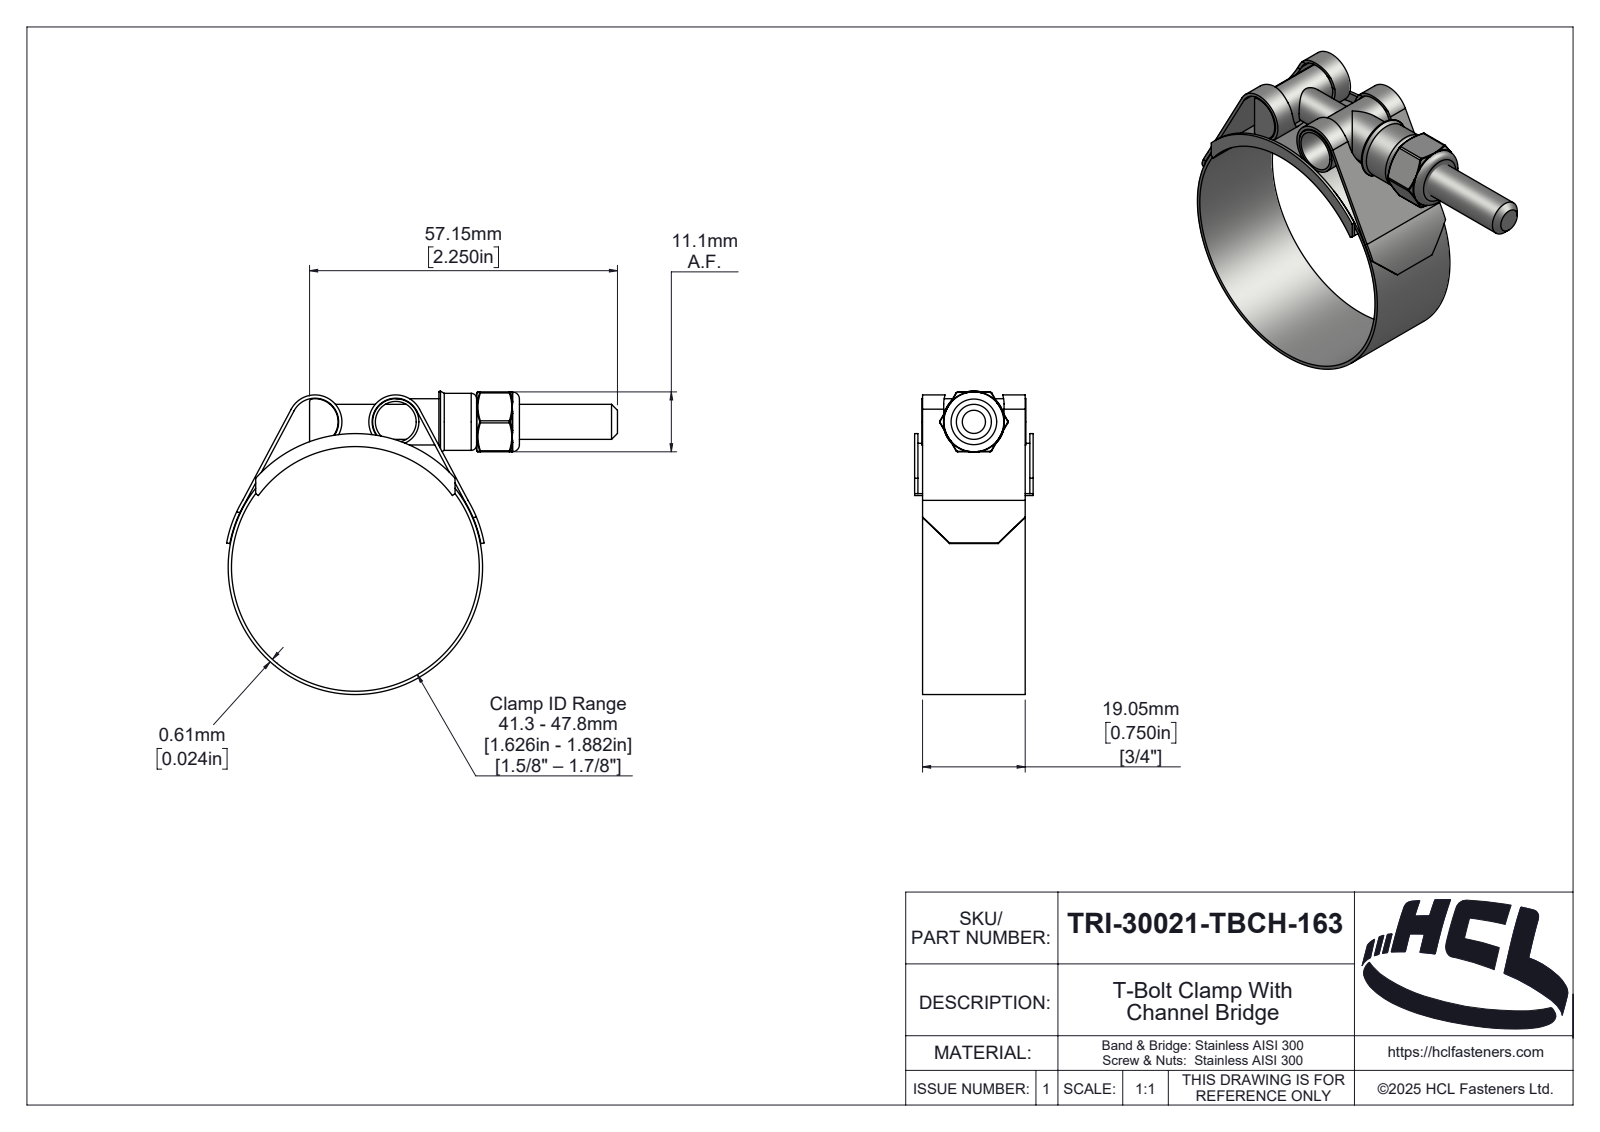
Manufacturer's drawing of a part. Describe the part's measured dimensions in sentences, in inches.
The part is named "TRI-30021-TBCH-163". Its 3-D file was written by "SolidWorks 2025 (AUTOMOTIVE_DESIGN)". It is 6 solids with 338 faces: 50 planar, 126 cylindrical and 162 other. Overall it measures 2.856 by 2.217 by 0.866 inches. Its volume is 0.409 cubic inches and its surface area 21.97 square inches. Round holes: 1 of diameter 0.213, 1 of diameter 0.25, 1 of diameter 0.256, 1 of diameter 0.298, 1 of diameter 1.811. Round bosses or shafts: 2 of diameter 0.338, 1 of diameter 1.859, 1 of diameter 0.417. Partial cylindrical surfaces (rounded edges, fillets, slot ends): 6 of radius 0.015, 2 of radius 0.02, 2 of radius 0.173, 2 of radius 0.197, 2 of radius 0.22, 1 of radius 0.023, 1 of radius 0.095, 1 of radius 0.119. The main face-to-face distances are 0.024, 0.058, 0.808, 0.029, 0.842, 0.034, 0.784, 0.75, 0.437, 0.866. The hole center spacings are 1.102.
